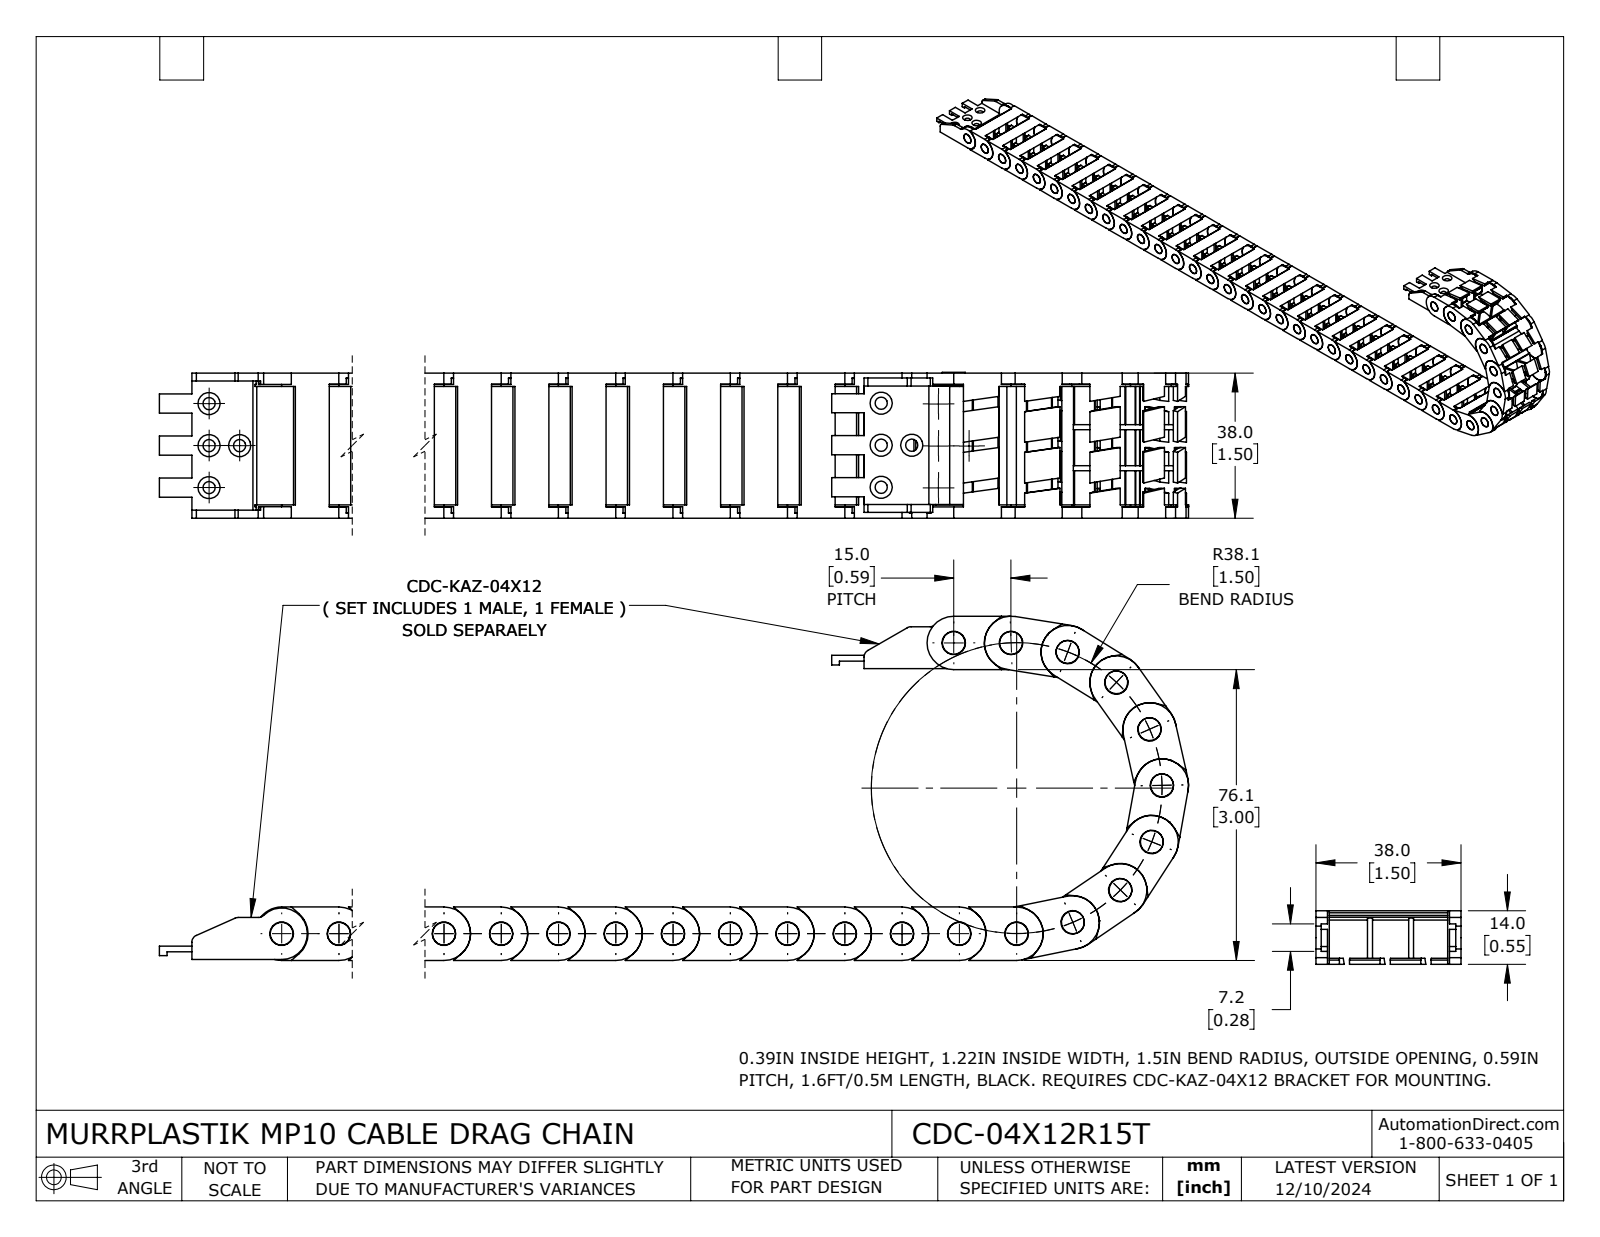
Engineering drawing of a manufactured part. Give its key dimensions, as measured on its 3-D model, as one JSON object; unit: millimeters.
{"part_name": "CDC-04X12R15T", "step_written_by": "SolidWorks 2024 (AUTOMOTIVE_DESIGN)", "units": "millimeters", "bodies": {"solids": 38, "faces": 3478, "planar": 2492, "cylindrical": 978, "other": 8}, "overall_size": [497.1, 90.1, 38.2], "volume_mm3": 91410, "surface_area_mm2": 129400, "round_holes": [[6.1, 36], [3.2, 8], [6.2, 1]], "round_bosses_or_shafts": [[6, 37], [14, 28]], "partial_cylinders_radius": [[0.5, 180], [7, 44], [3.6, 36], [11.6, 36], [7, 16], [2, 6], [1, 2], [6.8, 2]], "face_to_face_distances": [3.5, 34.5, 1.3, 14, 1.6, 38, 31, 2.2, 33.2, 36.7], "hole_center_spacings": [15, 30, 45, 60, 75, 90, 105, 120]}
